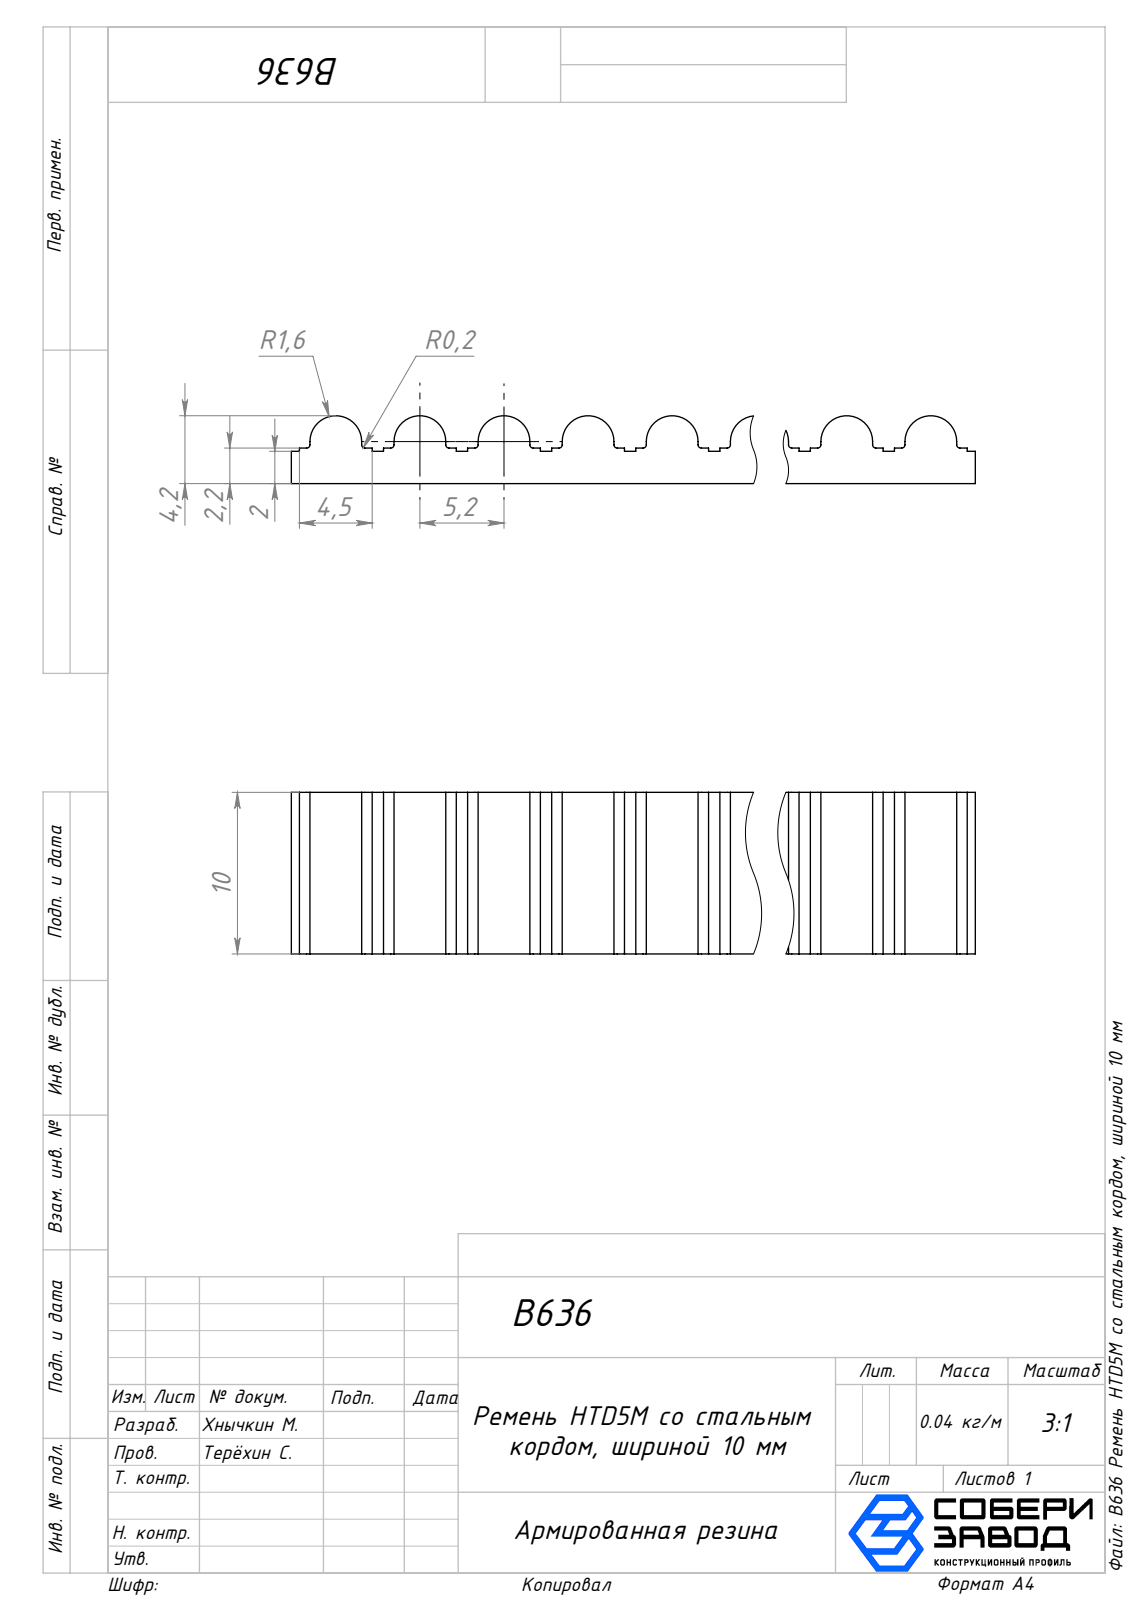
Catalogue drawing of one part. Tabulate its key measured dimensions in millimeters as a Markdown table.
| quantity | value |
| --- | --- |
| part name | B636 Ремень HTD5M со стальным кордом, шириной 10 мм |
| STEP written by | SolidWorks 2025 (AUTOMOTIVE_DESIGN) |
| units | millimeters |
| bodies | 1 solid, 86 faces (62 planar, 24 cylindrical, 0 other) |
| overall size | 41.9 × 10 × 4.2 |
| volume | 1 335 mm³ |
| surface area | 1 373 mm² |
| partial cylindrical surfaces (radius × count) | 0.2 × 16, 1.6 × 8 |
| main face-to-face distances | 10, 2, 2.2, 5.2, 10.4, 15.6, 41.9, 20.8, 3.2, 8.4 |
